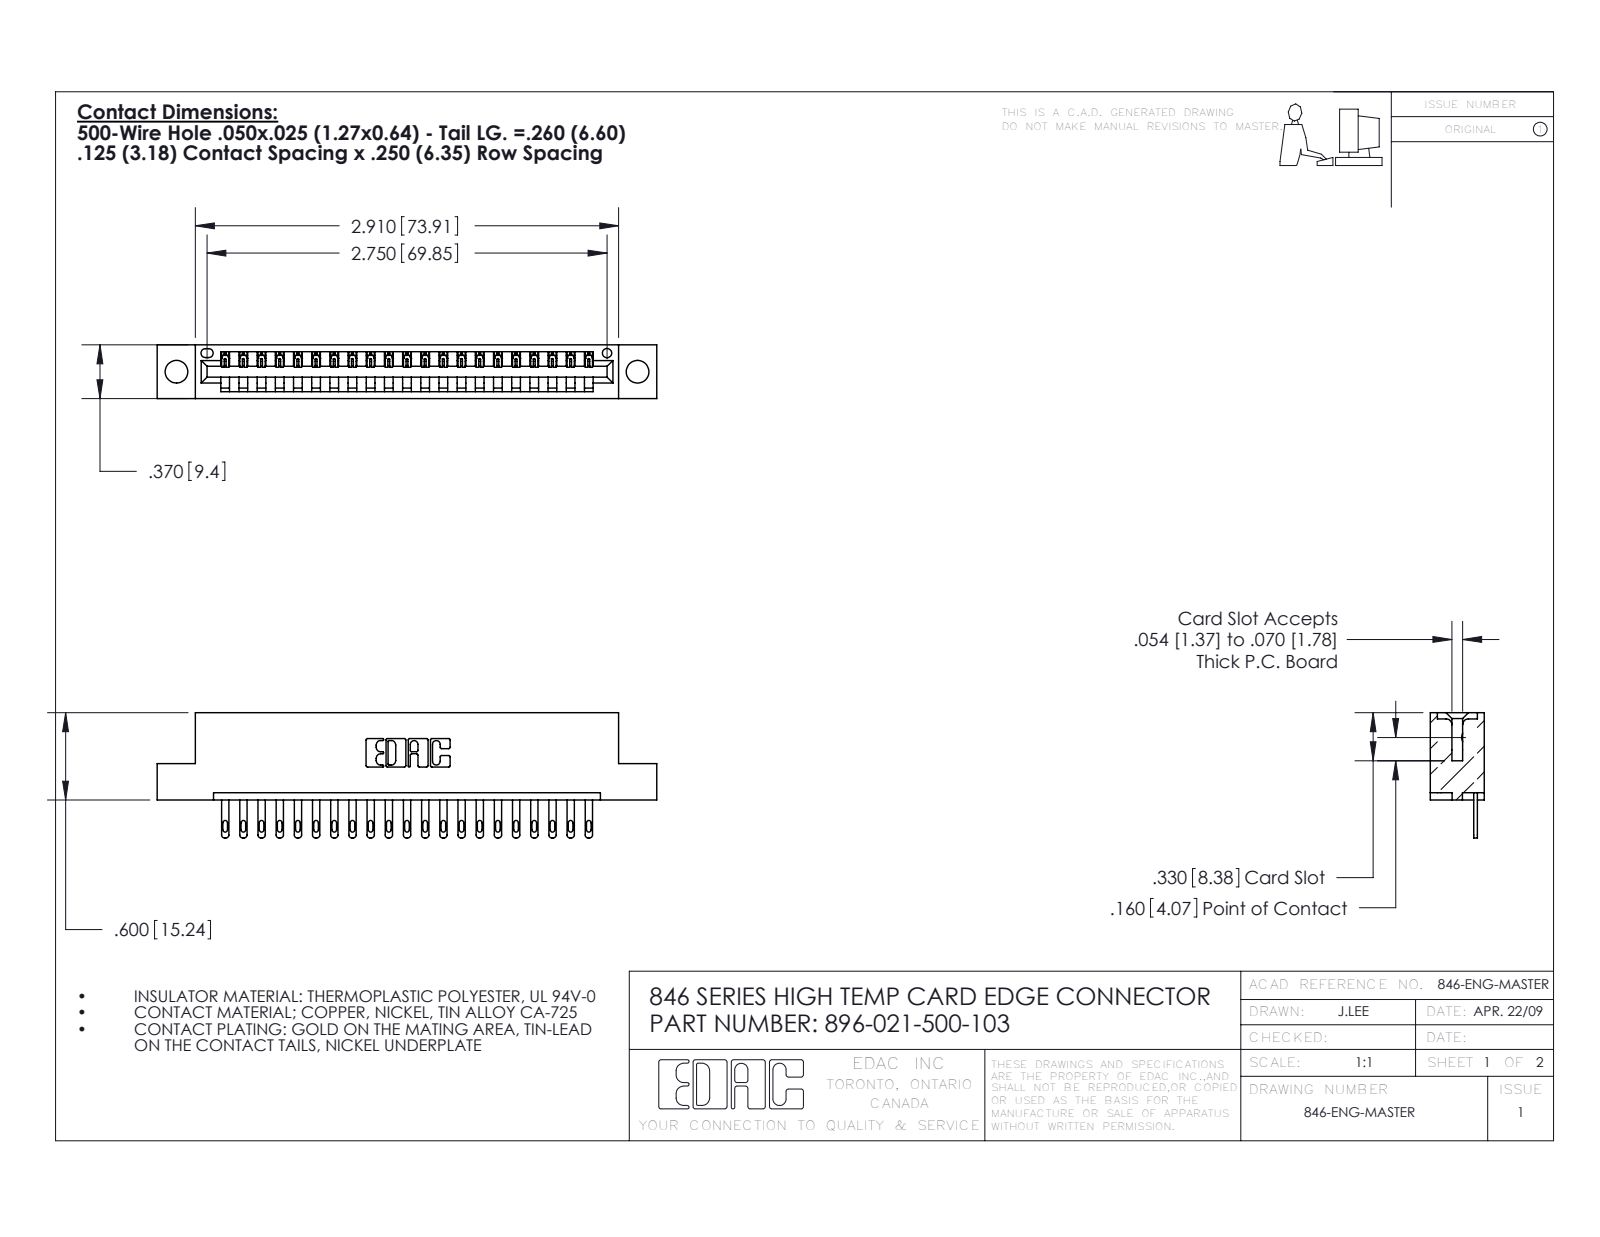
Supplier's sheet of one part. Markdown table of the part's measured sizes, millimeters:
| quantity | value |
| --- | --- |
| part name | 345-250-002_345-250-002-102; 345-292-001_345-293-100; 896-021-500-103; 846 Part_Flush Mounting Lugs - 0.156 Dia-TH |
| STEP written by | SolidWorks 2020 (CONFIG_CONTROL_DESIGN) |
| units | millimeters |
| bodies | 24 solids, 1294 faces (800 planar, 486 cylindrical, 8 other) |
| overall size | 87.2 × 21.8 × 9.4 |
| volume | 8 240 mm³ |
| surface area | 10 340 mm² |
| round holes (diameter × count) | 2.9 × 2, 4 × 2, 1.6 × 1 |
| round bosses / shafts (diameter × count) | 6.4 × 2, 4.6 × 2, 3.5 × 2 |
| partial cylindrical surfaces (radius × count) | 0.2 × 42, 0.4 × 42, 0.5 × 42, 0.3 × 22, 0.2 × 6, 0.8 × 6, 0.7 × 3, 0.8 × 2 |
| main face-to-face distances | 1.2, 8.2, 6.4, 9.4, 0.6, 1.8, 7.6, 3.8, 5.6, 2.5 |
| hole center spacings | 6.2, 75.3, 80.5 |
